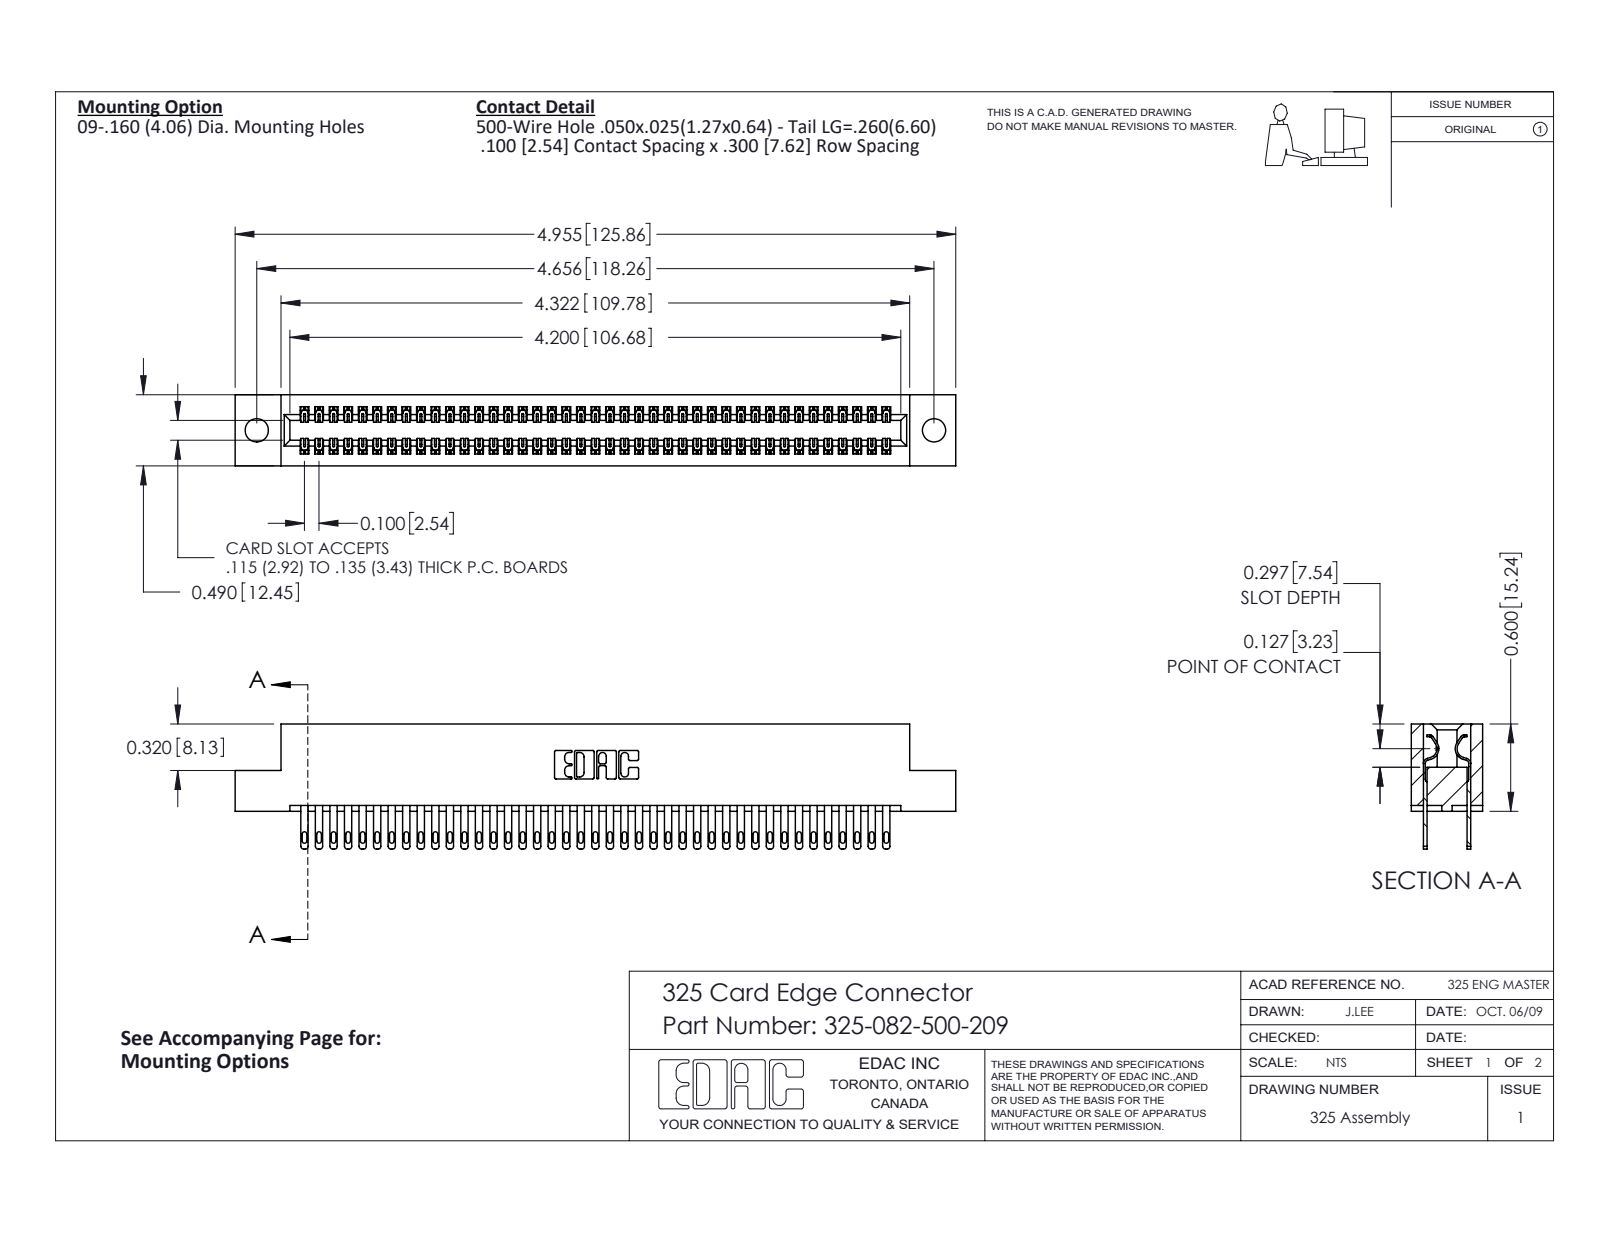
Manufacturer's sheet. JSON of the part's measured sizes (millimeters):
{"part_name": "325-082-500-209; 325 Part_.160 TH; 325-292-001_325-293-100", "step_written_by": "SolidWorks 2016 (CONFIG_CONTROL_DESIGN)", "units": "millimeters", "bodies": {"solids": 83, "faces": 4050, "planar": 2530, "cylindrical": 1520, "other": 0}, "overall_size": [125.9, 21.8, 12.4], "volume_mm3": 16300, "surface_area_mm2": 20430, "round_holes": [[4.1, 2]], "partial_cylinders_radius": [[0.2, 123], [0.4, 82], [0.5, 82], [0.3, 22], [0.2, 6], [0.8, 6], [0.7, 3], [0.4, 2]], "face_to_face_distances": [2.1, 10.3, 7.6, 2.7, 9.7, 0.6, 12.4, 8.3, 7, 14.2], "hole_center_spacings": [118.3]}
